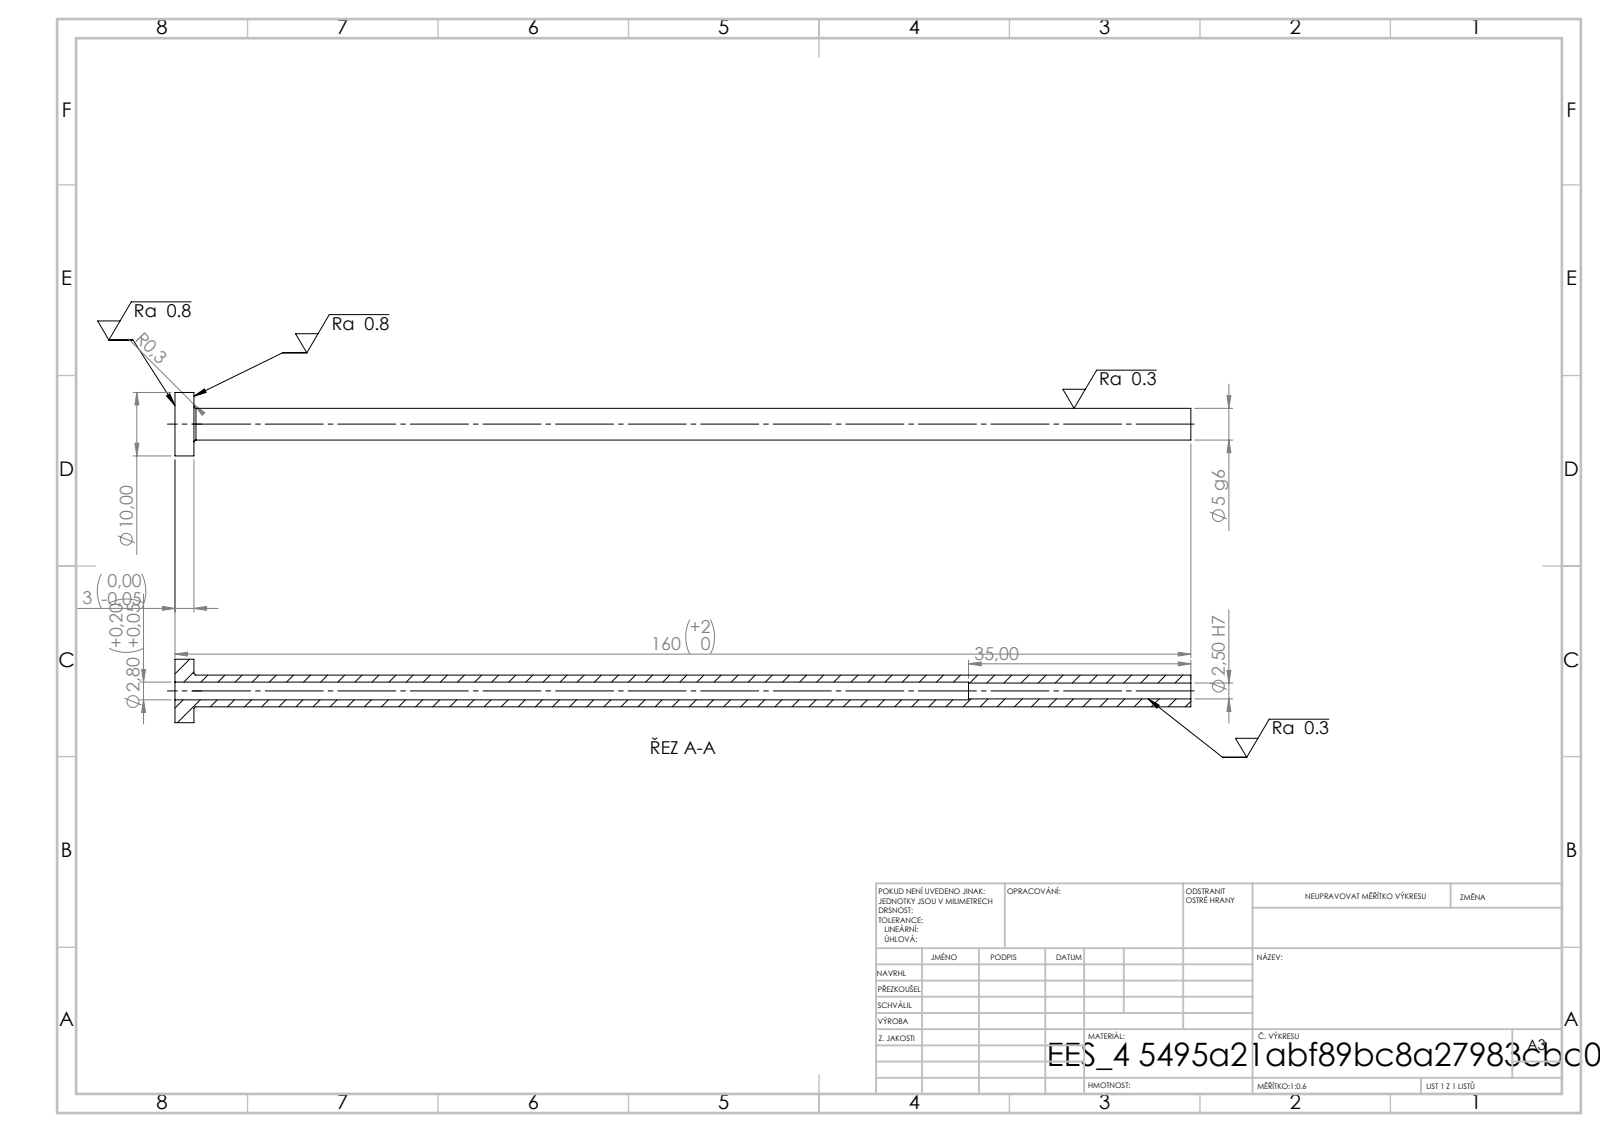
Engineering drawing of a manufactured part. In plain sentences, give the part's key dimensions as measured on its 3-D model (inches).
Its 3-D file was written by "SolidWorks 2019 (CONFIG_CONTROL_DESIGN)". It is 1 solid with 14 faces: 4 planar, 8 cylindrical and 2 other. Overall it measures 6.299 by 0.394 by 0.394 inches. Its volume is 0.145 cubic inches and its surface area 6.324 square inches. Round holes: 1 of diameter 0.098, 1 of diameter 0.11. Round bosses or shafts: 1 of diameter 0.394, 1 of diameter 0.197. The main face-to-face distances are 0.118, 6.299, 6.181, 4.921, 4.803, 1.378.
